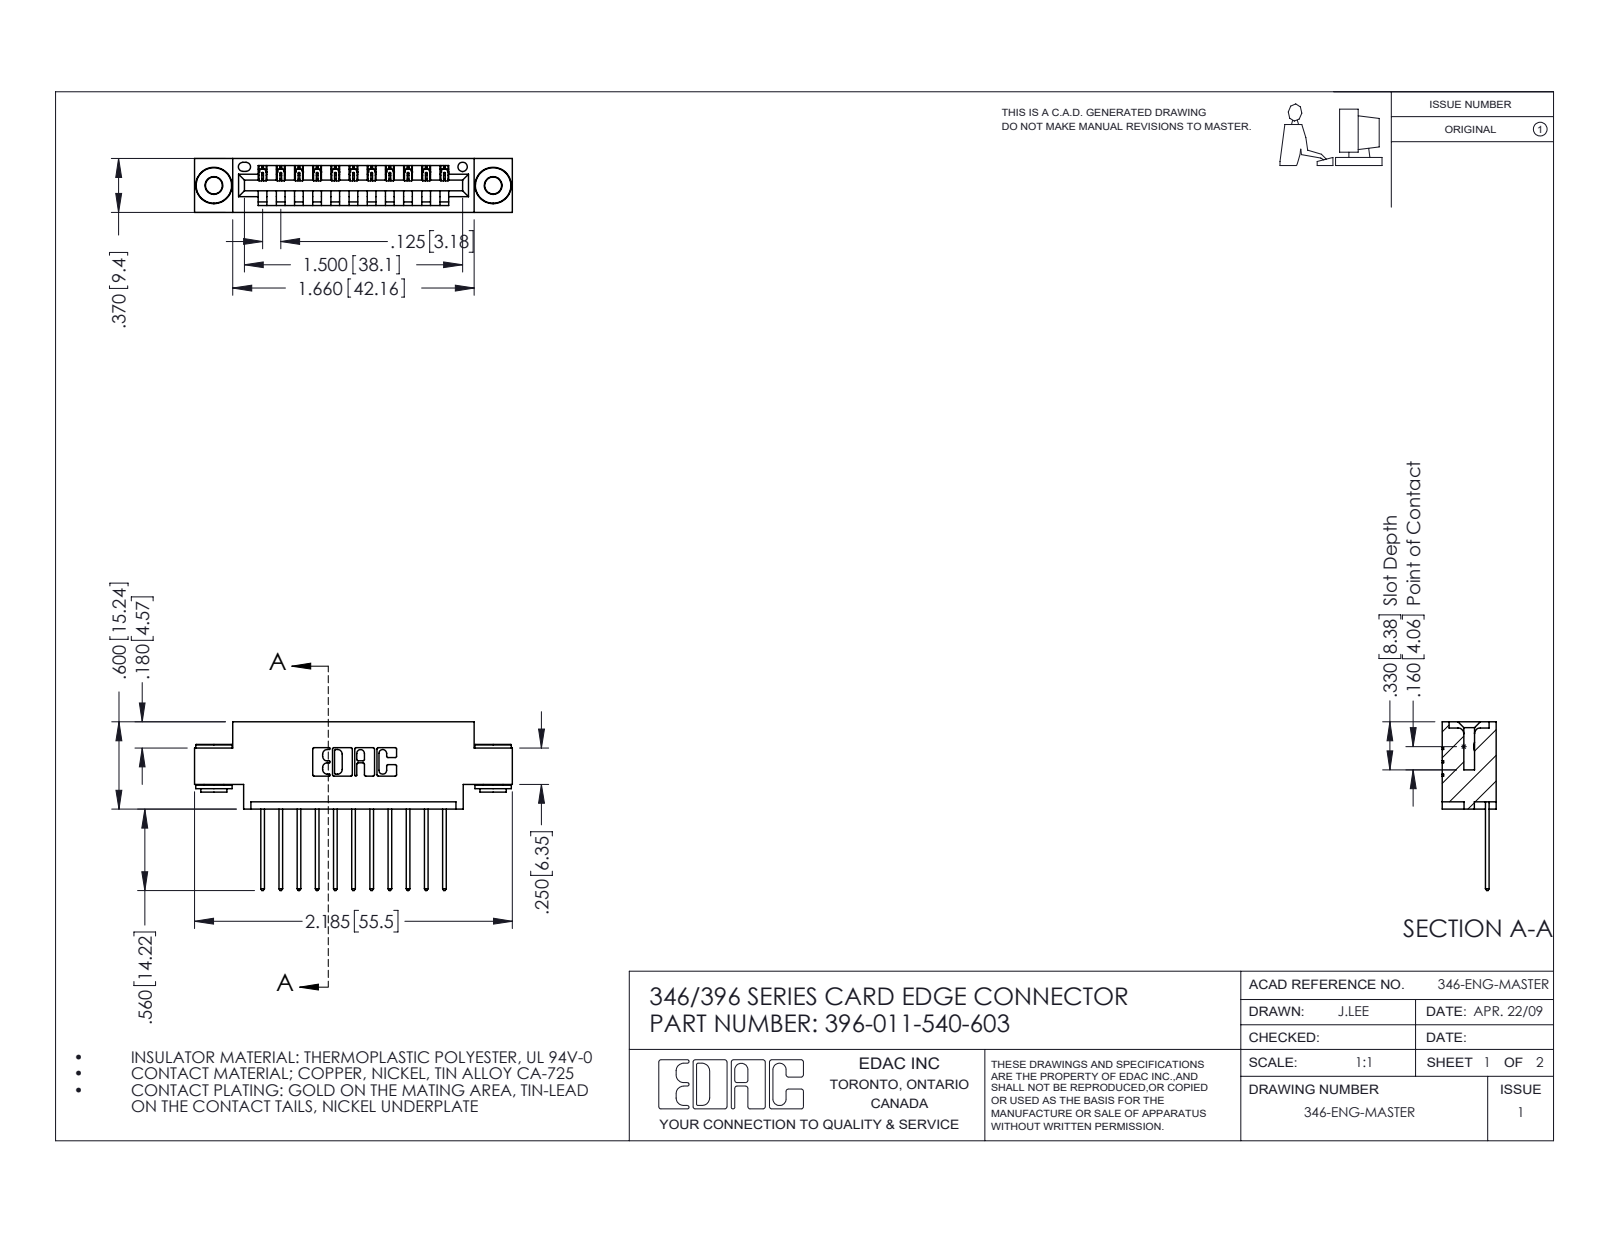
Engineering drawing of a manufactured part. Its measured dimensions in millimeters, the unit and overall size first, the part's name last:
Units: millimetres
Overall size (bounding box): 55.5 × 29.5 × 9.4
Round holes (diameter × count): ⌀2.9 ×2, ⌀4 ×2, ⌀1.6 ×1
Round bosses / shafts (diameter × count): ⌀6.4 ×2, ⌀4.6 ×2, ⌀3.5 ×2
Partial cylindrical surfaces — rounded edges, fillets, slot ends (radius × count): R0.2 ×22, R0.3 ×22, R0.3 ×22, R0.2 ×6, R0.8 ×6, R0.7 ×3, R0.8 ×2, R1 ×2
Main face-to-face distances: 6.4, 9.4, 1.2, 8.2, 0.6, 1.8, 7.6, 3.8, 5.6, 2.5
Hole centre spacings: 6.2, 43.6, 48.8
Volume: 4 980 mm³ · Surface area: 6 376 mm²
Bodies: 14 solids, 802 faces (530 planar, 264 cylindrical, 8 other)
Part name (STEP PRODUCT): 345-250-002_345-250-002-102; 345-292-001_345-293-140; 396-011-540-603; 346 Part_0.170 Offset - 0.156 Dia-TH
STEP written by: SolidWorks 2016 (CONFIG_CONTROL_DESIGN)
